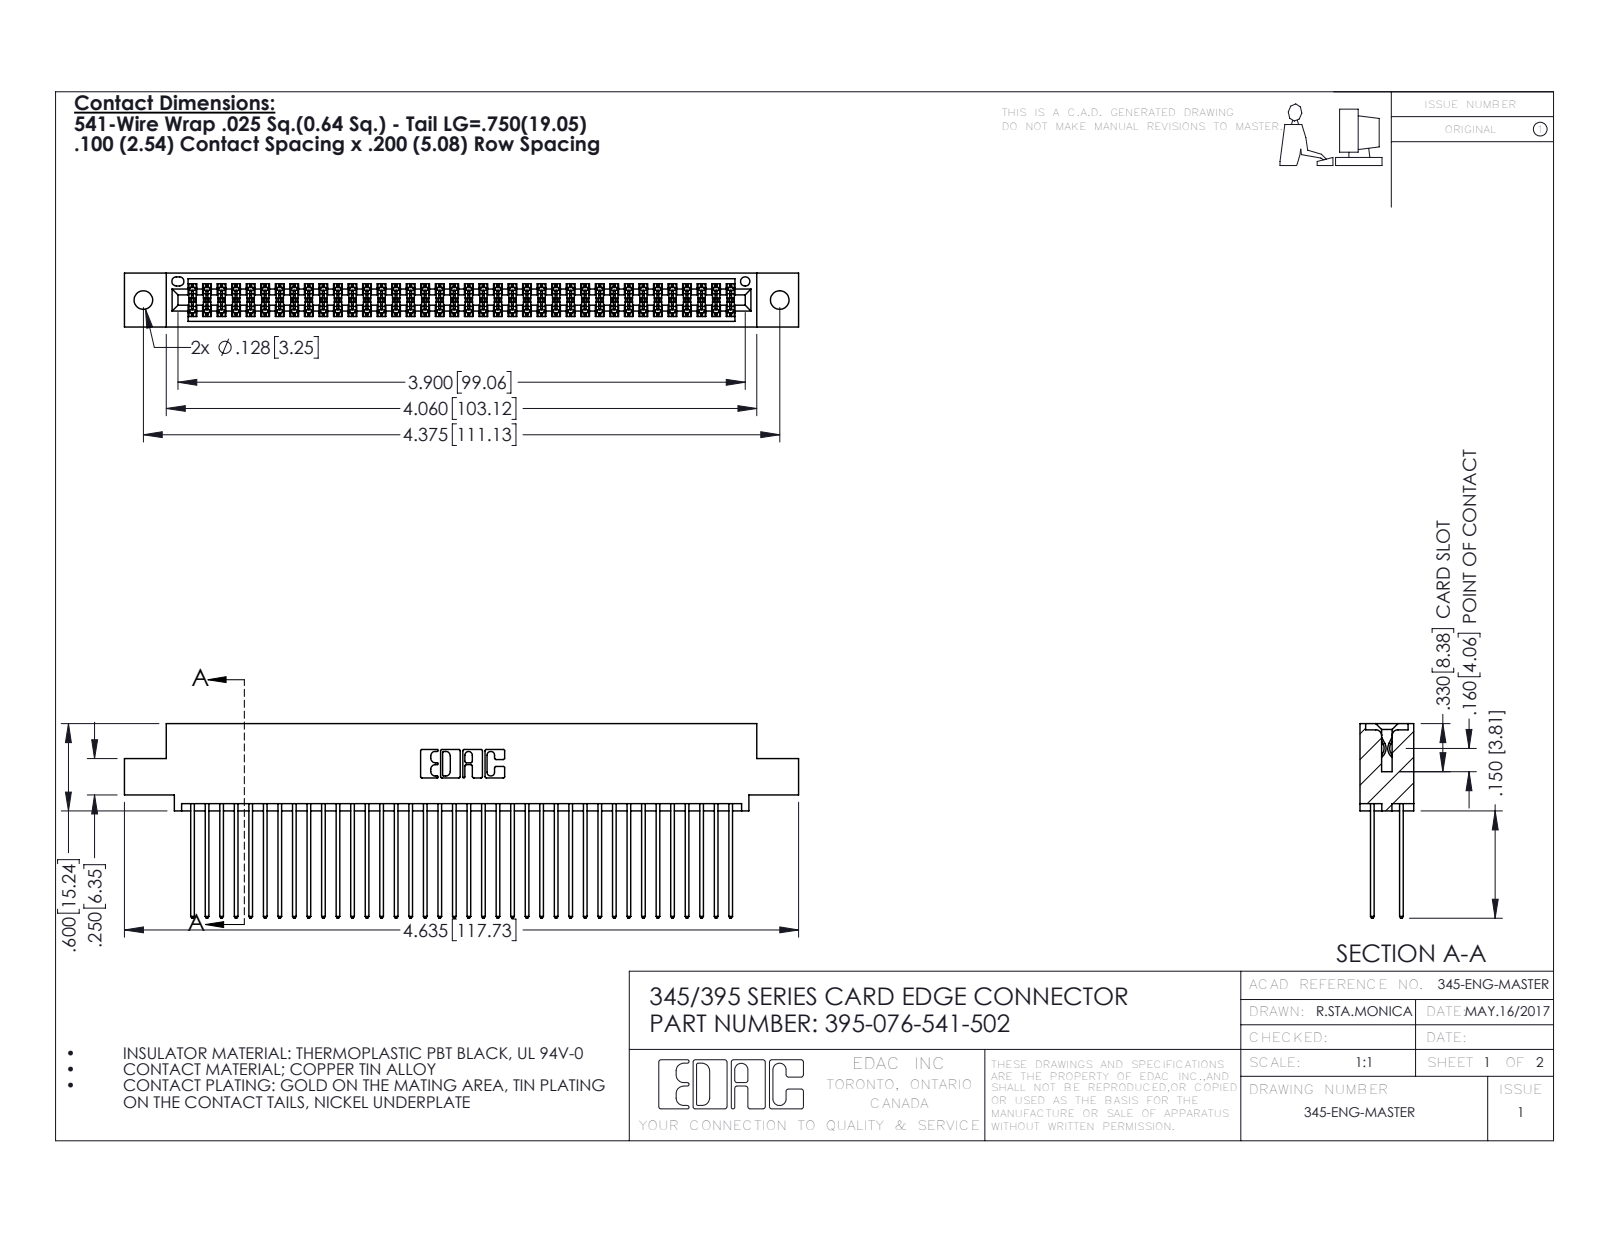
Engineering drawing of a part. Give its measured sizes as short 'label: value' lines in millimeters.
name: 345 Part_0.110 Offset - 0.128 Dia; 345-292-001_345-293-141; 395-076-541-502
written by: SolidWorks 2016 (CONFIG_CONTROL_DESIGN)
unit: mm
bodies: 77 solids, 3930 faces (2592 planar, 1338 cylindrical, 0 other)
size: 117.7 × 34 × 9.4
volume: 11 700 mm³; area: 19 120 mm²
holes: 2× ⌀3.3, 1× ⌀1.6
rounds: 114× R0.2, 76× R0.3, 22× R0.3, 6× R0.2, 6× R0.8, 3× R0.7, 2× R0.4, 2× R0.5
face distances: 7.6, 1.8, 5.1, 2.5, 6.9, 0.6, 5.7, 9.4, 4.4, 3.8
hole spacings: 6.9, 105.1, 111.1
